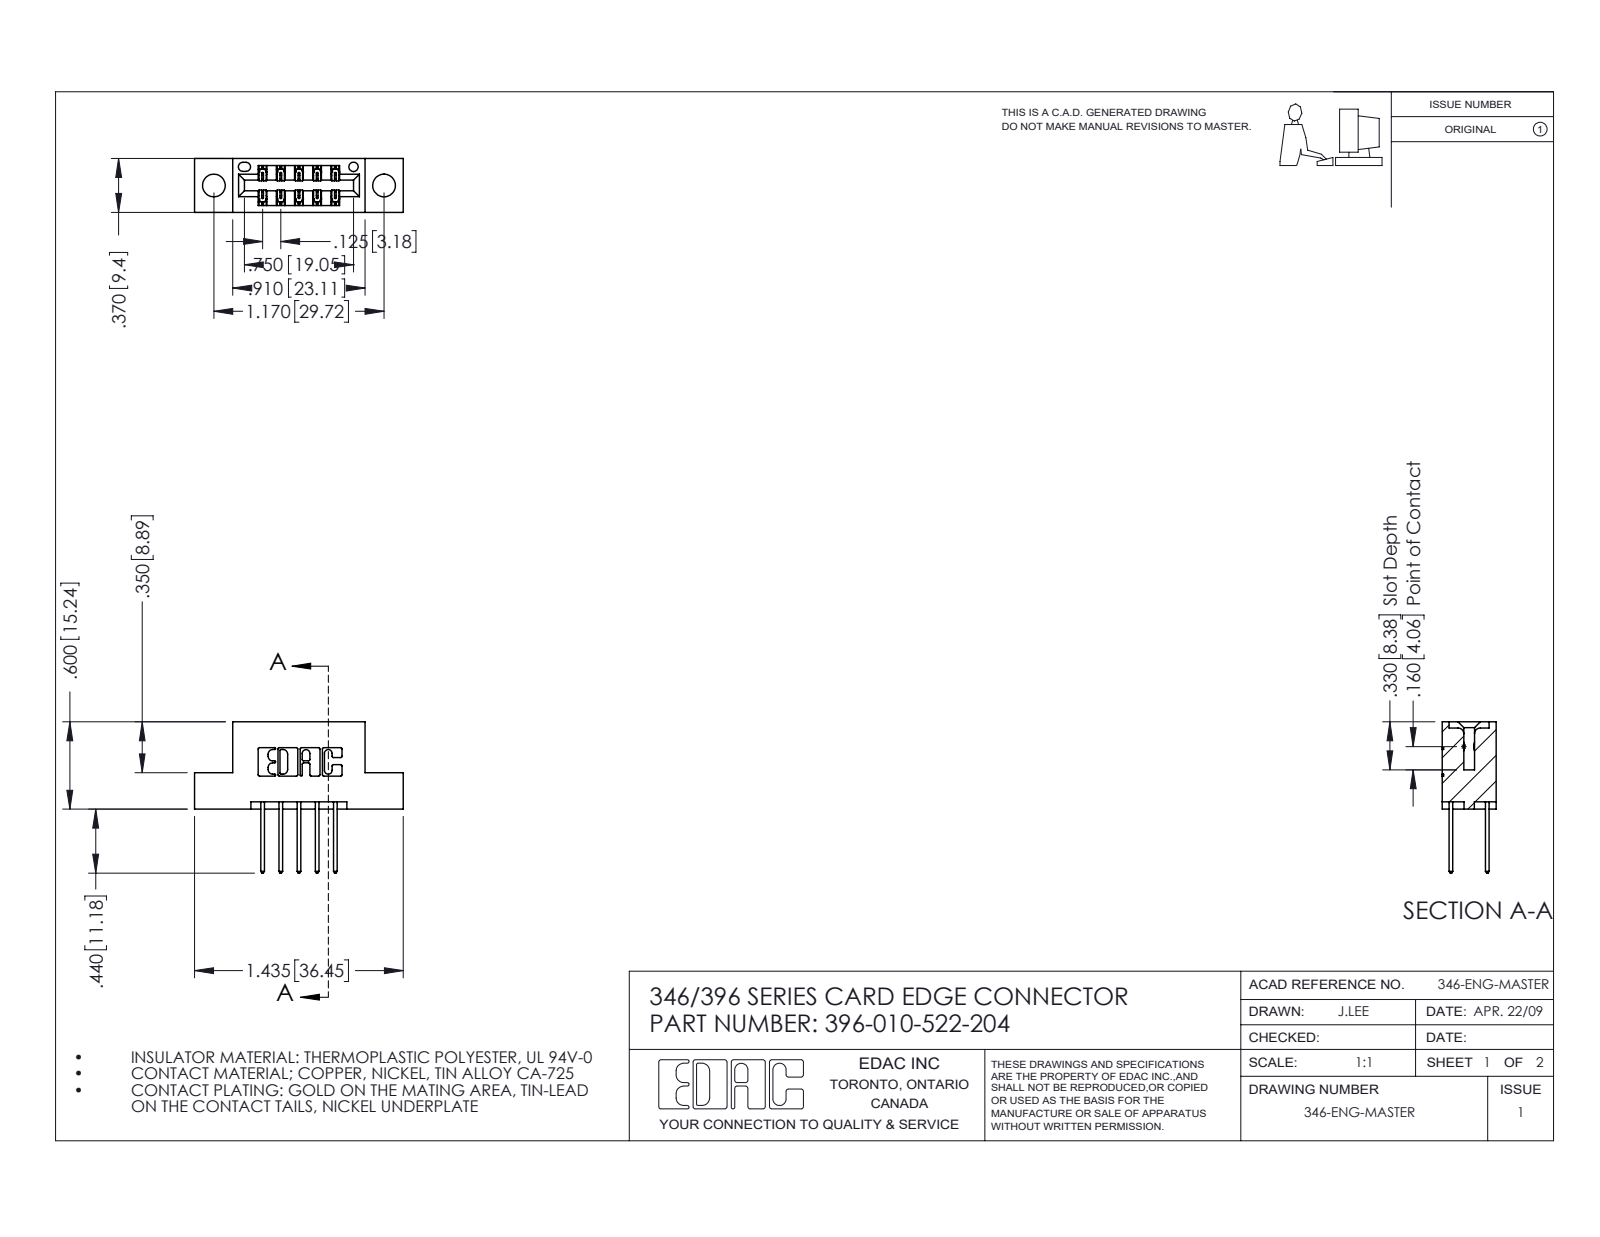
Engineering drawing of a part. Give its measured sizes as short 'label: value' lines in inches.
name: 396-010-522-204; 346 Part_Flush Mounting Lugs - 0.156 Dia-TH; 345-292-001_345-293-122
written by: SolidWorks 2016 (CONFIG_CONTROL_DESIGN)
unit: in
bodies: 11 solids, 642 faces (426 planar, 216 cylindrical, 0 other)
size: 1.435 × 1.04 × 0.37
volume: 0.196 in³; area: 5.821 in²
holes: 2× ⌀0.156, 1× ⌀0.064
rounds: 22× R0.01, 15× R0.006, 10× R0.01, 6× R0.007, 6× R0.031, 3× R0.026, 2× R0.014, 2× R0.022
face distances: 0.25, 0.048, 0.322, 0.37, 0.025, 0.072, 0.298, 0.275, 0.148, 0.222
hole spacings: 0.246, 0.969, 1.17
